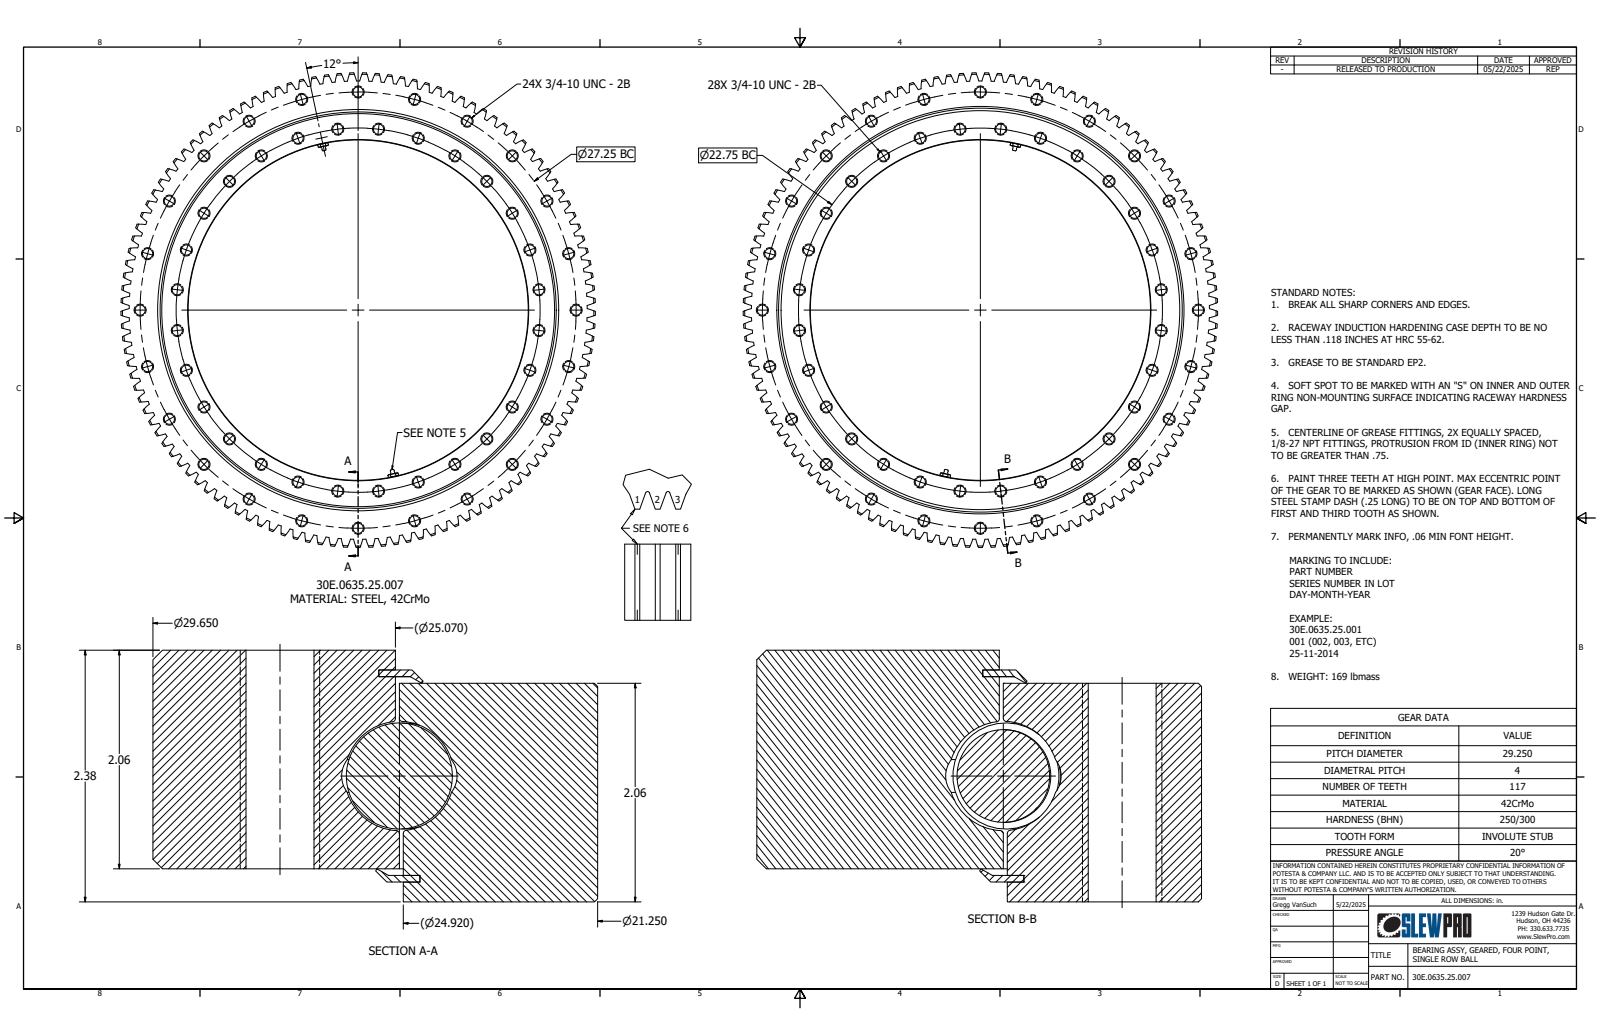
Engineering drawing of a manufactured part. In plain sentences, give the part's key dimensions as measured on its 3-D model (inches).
The part is named "30E.0635.25.001; Spur Gears1; HGF_11". Its 3-D file was written by "Autodesk Inventor 2026 (AUTOMOTIVE_DESIGN)". It is 8 solids with 1013 faces: 38 planar, 540 cylindrical and 435 other. Overall it measures 29.65 by 29.647 by 2.375 inches. Its volume is 596.6 cubic inches and its surface area 2 158 square inches. Round holes: 52 of diameter 0.642, 2 of diameter 0.063, 2 of diameter 0.109, 1 of diameter 1.126, 1 of diameter 21.25, 1 of diameter 24.607, 1 of diameter 24.995, 1 of diameter 25.07, 1 of diameter 25.383. Round bosses or shafts: 1 of diameter 25.383, 1 of diameter 24.92, 1 of diameter 24.607, 1 of diameter 1.125. Partial cylindrical surfaces (rounded edges, fillets, slot ends): 234 of radius 3.607, 1 of radius 14.312, 1 of radius 14.825. The main face-to-face distances are 2.063, 0.312, 1.751, 2.375, 1.939, 0.063, 0.187, 2.188, 0.125, 1.876. The hole center spacings are 13.625, 7.053, 25.176, 26.321, 3.557, 10.428, 16.589, 19.269.
